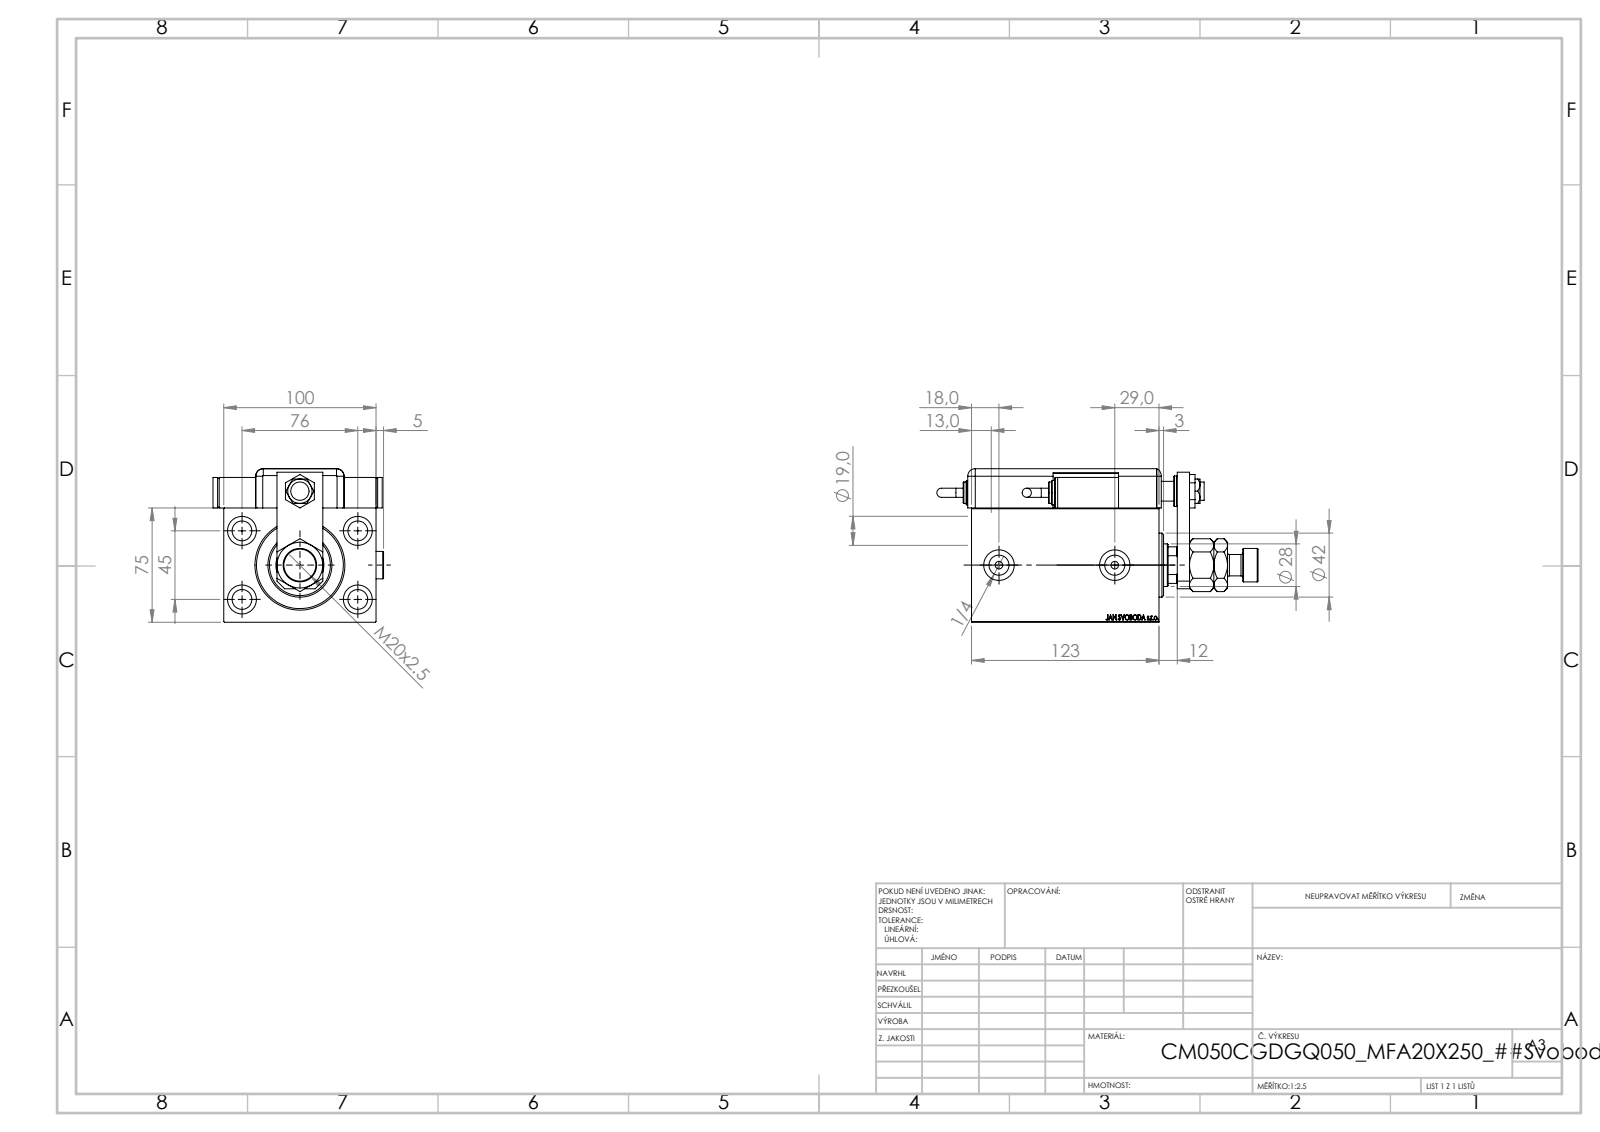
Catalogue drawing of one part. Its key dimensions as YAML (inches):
part_name: "ZARAZKA_Q; SWITCH_Q_FRONT_BACK; NUT_D13; TYC (+7 more)"
step_written_by: "SolidWorks 2019 (CONFIG_CONTROL_DESIGN)"
units: inches
bodies: {solids: 16, faces: 1355, planar: 665, cylindrical: 137, other: 553}
overall_size: [8.298, 4.406, 3.969]
volume: 57.83
surface_area: 299.9
round_holes:
  - {diameter: 0.512, count: 5}
  - {diameter: 0.748, count: 4}
  - {diameter: 0.787, count: 3}
  - {diameter: 0.157, count: 2}
  - {diameter: 0.197, count: 2}
  - {diameter: 0.315, count: 2}
  - {diameter: 0.518, count: 2}
  - {diameter: 0.472, count: 1}
  - {diameter: 0.551, count: 1}
  - {diameter: 0.728, count: 1}
  - {diameter: 1.102, count: 1}
  - {diameter: 1.24, count: 1}
round_bosses_or_shafts:
  - {diameter: 0.787, count: 3}
  - {diameter: 0.551, count: 3}
  - {diameter: 0.709, count: 2}
  - {diameter: 0.63, count: 2}
  - {diameter: 0.236, count: 2}
  - {diameter: 1.654, count: 1}
  - {diameter: 0.866, count: 1}
partial_cylinders:
  - {radius: 0.197, count: 9}
  - {radius: 0.394, count: 1}
  - {radius: 0.531, count: 1}
face_to_face_distances: [2.953, 0.118, 3.937, 0.787, 0.551, 1.016, 3.969, 0.531, 4.843, 4.291]
hole_center_spacings: [1.739, 2.992, 1.772, 1.813, 3.17, 3.477, 0.787, 1.909]
